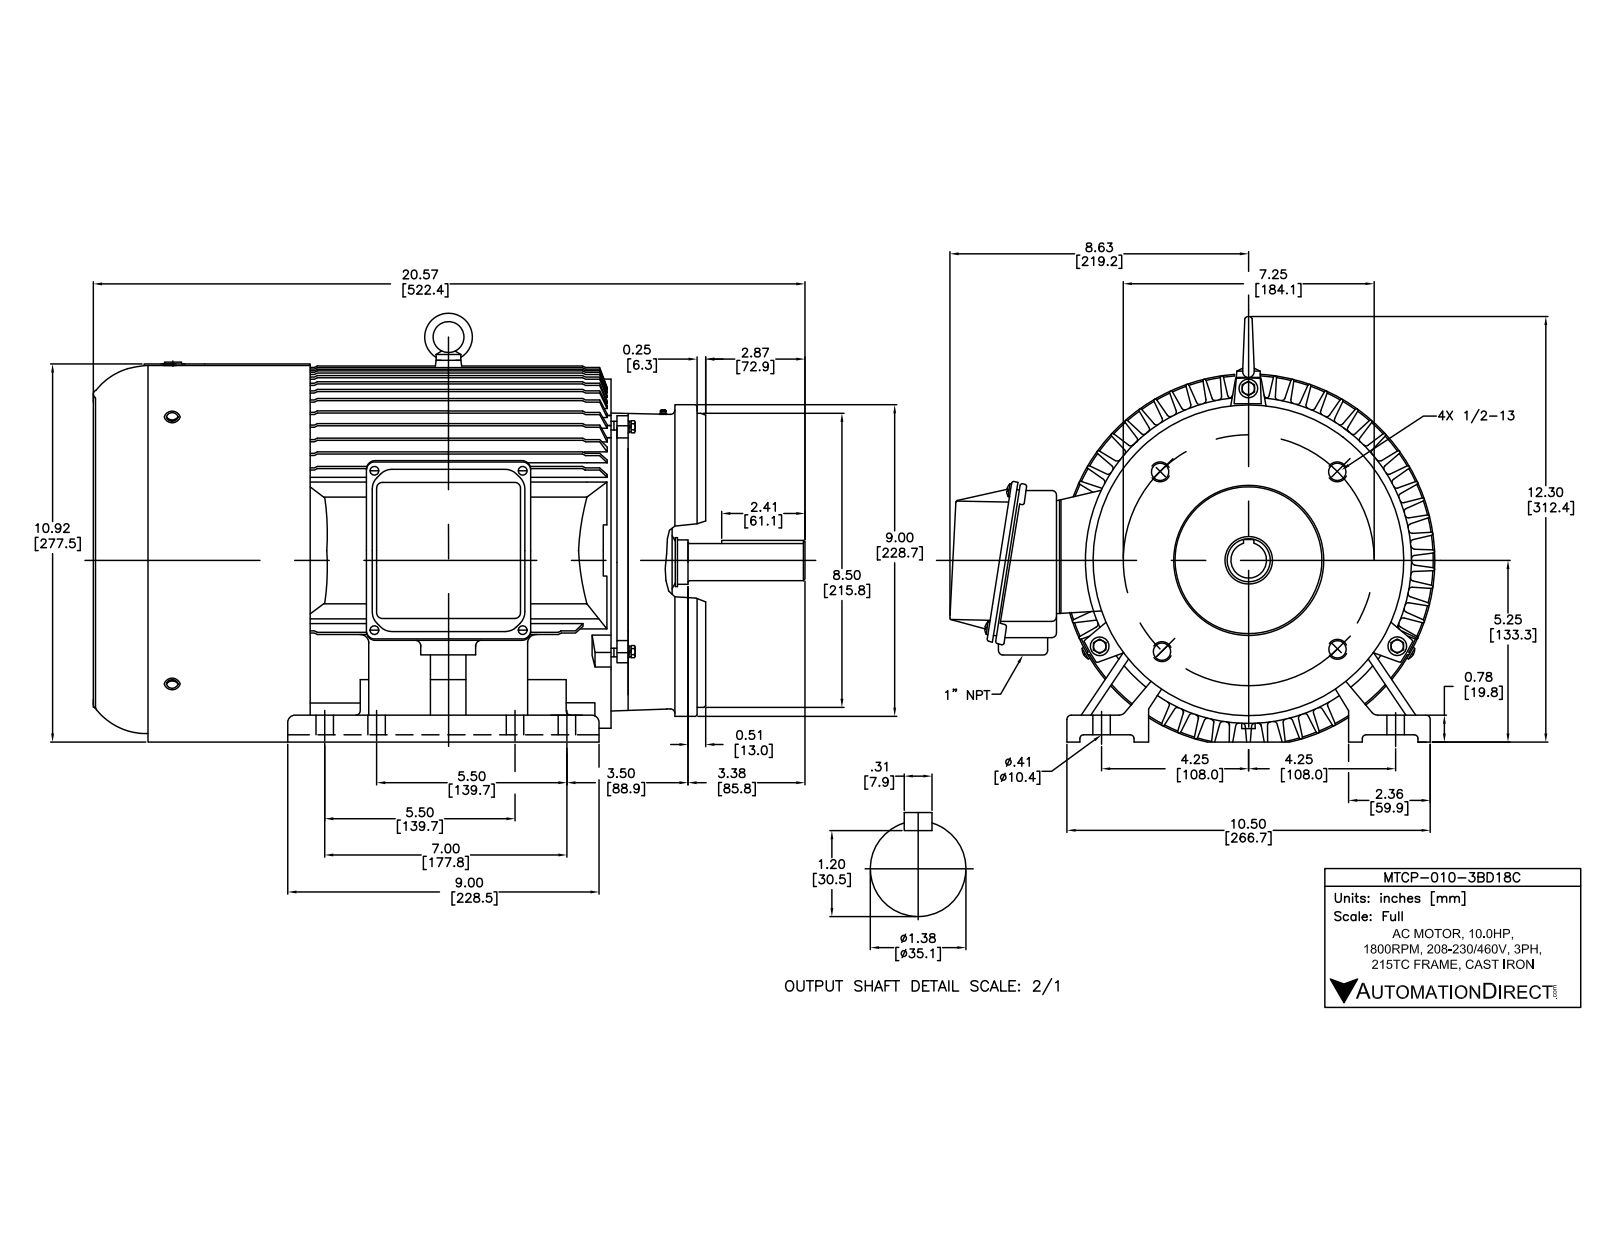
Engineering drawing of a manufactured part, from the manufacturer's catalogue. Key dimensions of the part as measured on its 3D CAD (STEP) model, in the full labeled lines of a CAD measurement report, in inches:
Part name (STEP PRODUCT): PE210接线盒座_默认_按加工; spring lock washers--normal type gb_GB_FASTENER_WASHER_SW 5; plain washers-chamfered--normal series-a gb_GB_FASTENER_WASHER_SWCA 5; MTCP215TC (+6 more)
STEP written by: SolidWorks 2017 (AUTOMOTIVE_DESIGN)
Units: inches
Bodies: 48 solids, 2707 faces (762 planar, 1003 cylindrical, 942 other)
Overall size (bounding box): 20.427 × 14.291 × 12.892
Volume: 276 in³ · Surface area: 2 602 in²
Round holes (diameter × count): ⌀0.228 ×14, ⌀0.165 ×11, ⌀0.354 ×8, ⌀0.079 ×4, ⌀0.422 ×4, ⌀0.197 ×3, ⌀0.209 ×3, ⌀0.213 ×3, ⌀0.331 ×3, ⌀0.342 ×3, ⌀0.394 ×3, ⌀0.268 ×1
Round bosses / shafts (diameter × count): ⌀0.197 ×8, ⌀0.315 ×6, ⌀0.394 ×4, ⌀0.63 ×3, ⌀0.507 ×3, ⌀11.354 ×1, ⌀10 ×1, ⌀8.898 ×1
Partial cylindrical surfaces — rounded edges, fillets, slot ends (radius × count): R0.039 ×239, R0.02 ×67, R0.118 ×60, R0.049 ×39, R0.276 ×28, R0.079 ×16, R0.315 ×11, R0.059 ×8
Main face-to-face distances: 0.197, 0.047, 0.236, 13.524, 2.939, 2.986, 3.222, 3.175, 0.079, 17.175
Hole centre spacings: 2.677, 3.786, 2.678, 3.937, 1, 3.625, 4.933, 5.127
